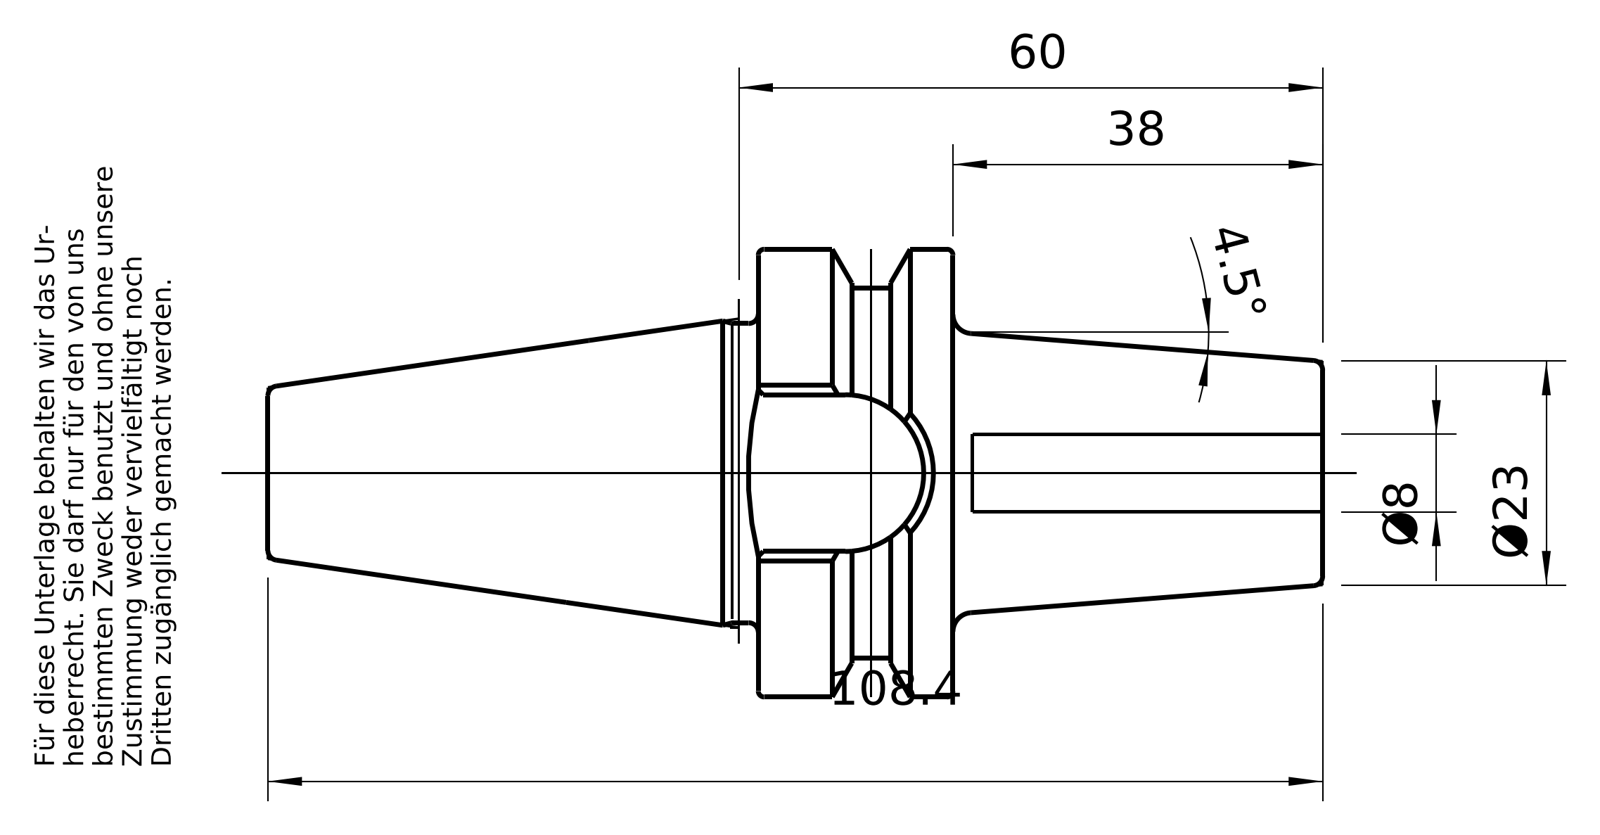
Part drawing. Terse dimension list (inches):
name: 30-645-08
written by: PRO/ENGINEER BY PARAMETRIC TECHNOLOGY CORPORATION, 2010430 (CONFIG_CONTROL_DESIGN)
unit: in
bodies: 1 solid, 94 faces (26 planar, 20 cylindrical, 48 other)
size: 4.268 × 1.81 × 1.81
volume: 4.151 in³; area: 24.07 in²
holes: 1× ⌀0.315, 1× ⌀0.398, 1× ⌀0.493, 1× ⌀0.512
bosses: 1× ⌀1.81, 1× ⌀1.211, 1× ⌀0.473
rounds: 1× R0.319, 1× R0.743
face distances: 0.787, 2.283, 1.496, 1.272, 0.638, 0.866, 0.079, 1.417, 1.984, 2.772
